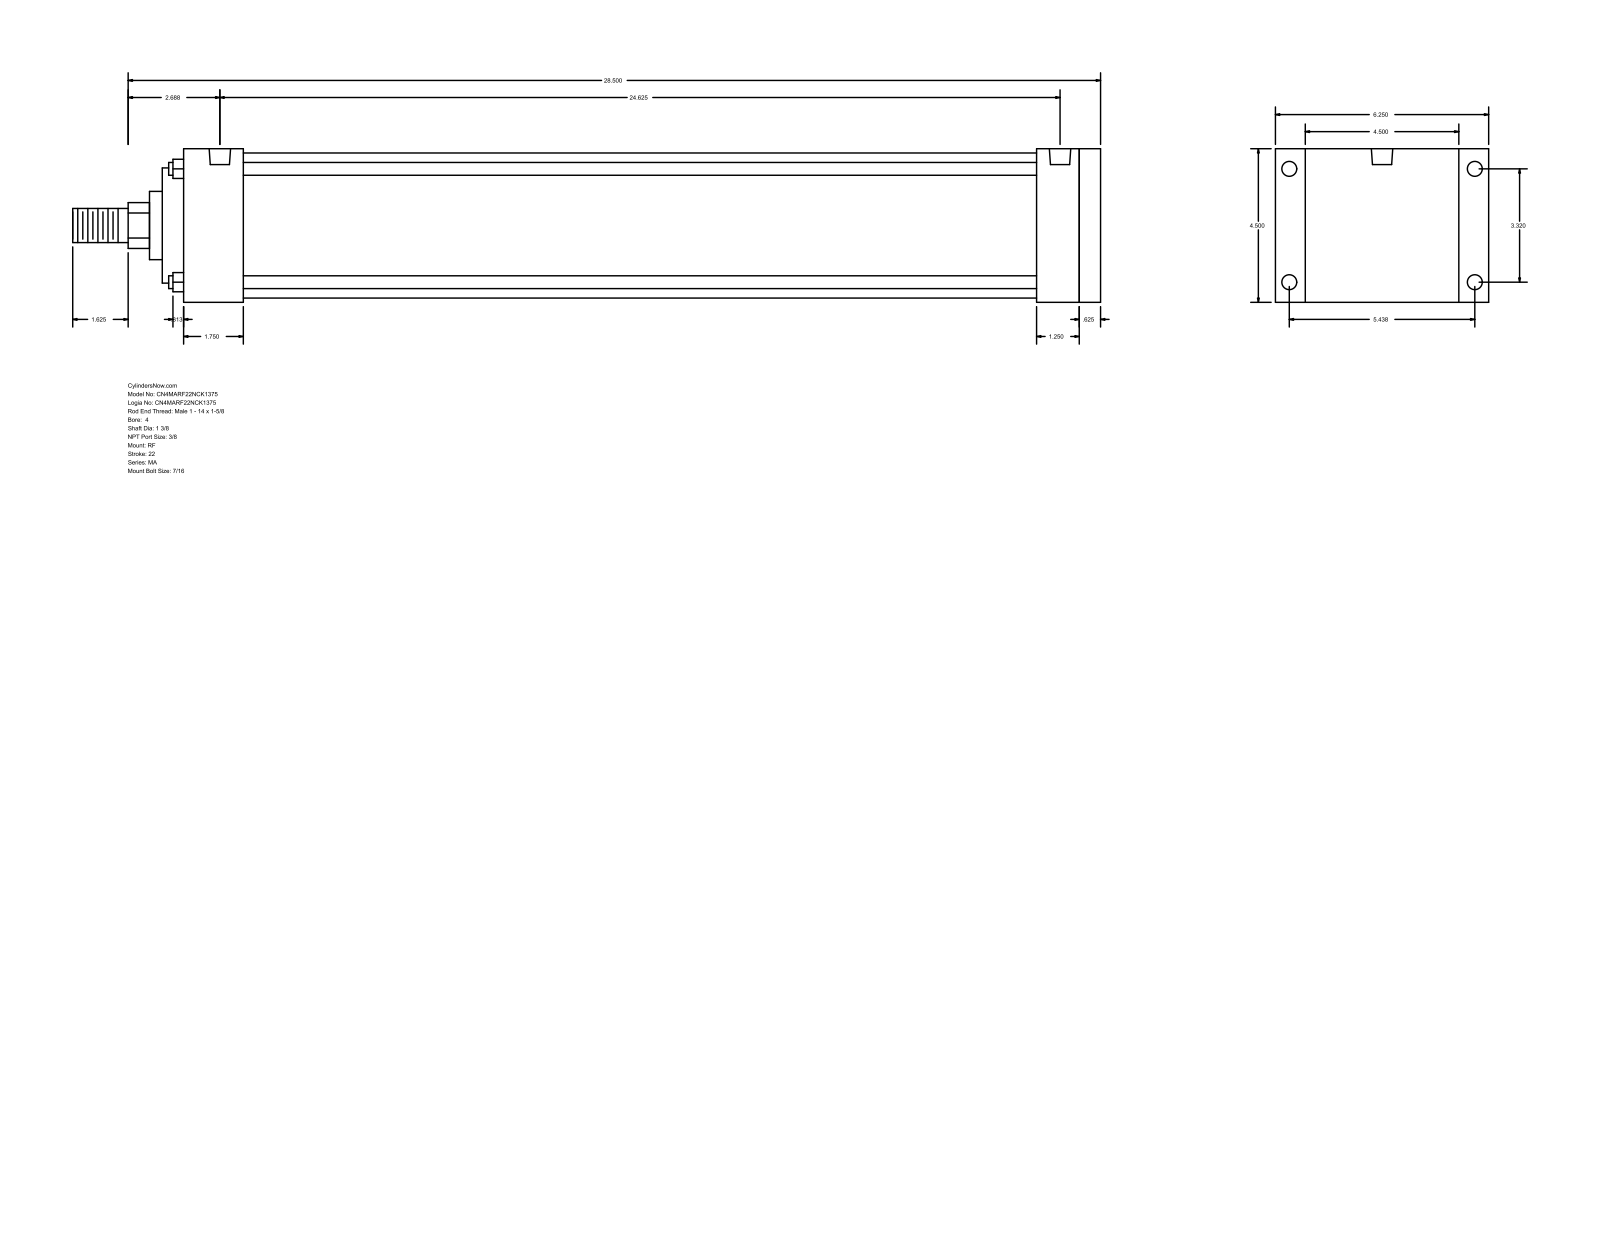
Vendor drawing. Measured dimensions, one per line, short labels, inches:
name: MA_RF__0400_1.375
written by: GSSL Pune (CONFIG_CONTROL_DESIGN)
unit: in
bodies: 0 solids, 94 faces (65 planar, 29 cylindrical, 0 other)
size: 30.125 × 6.25 × 4.5
holes: 8× ⌀0.437, 2× ⌀0.627
bosses: 4× ⌀0.375, 1× ⌀4.25, 1× ⌀3.375, 1× ⌀2, 1× ⌀1.375, 1× ⌀1
rounds: 1× R0.672
face distances: 4.5, 26.875, 0.625, 26.25, 0.625, 26.875, 27.5, 0.875, 5.375, 25.625
hole spacings: 3.32, 5.438, 6.371, 24.25, 0.187, 0.188, 24.437, 24.438
